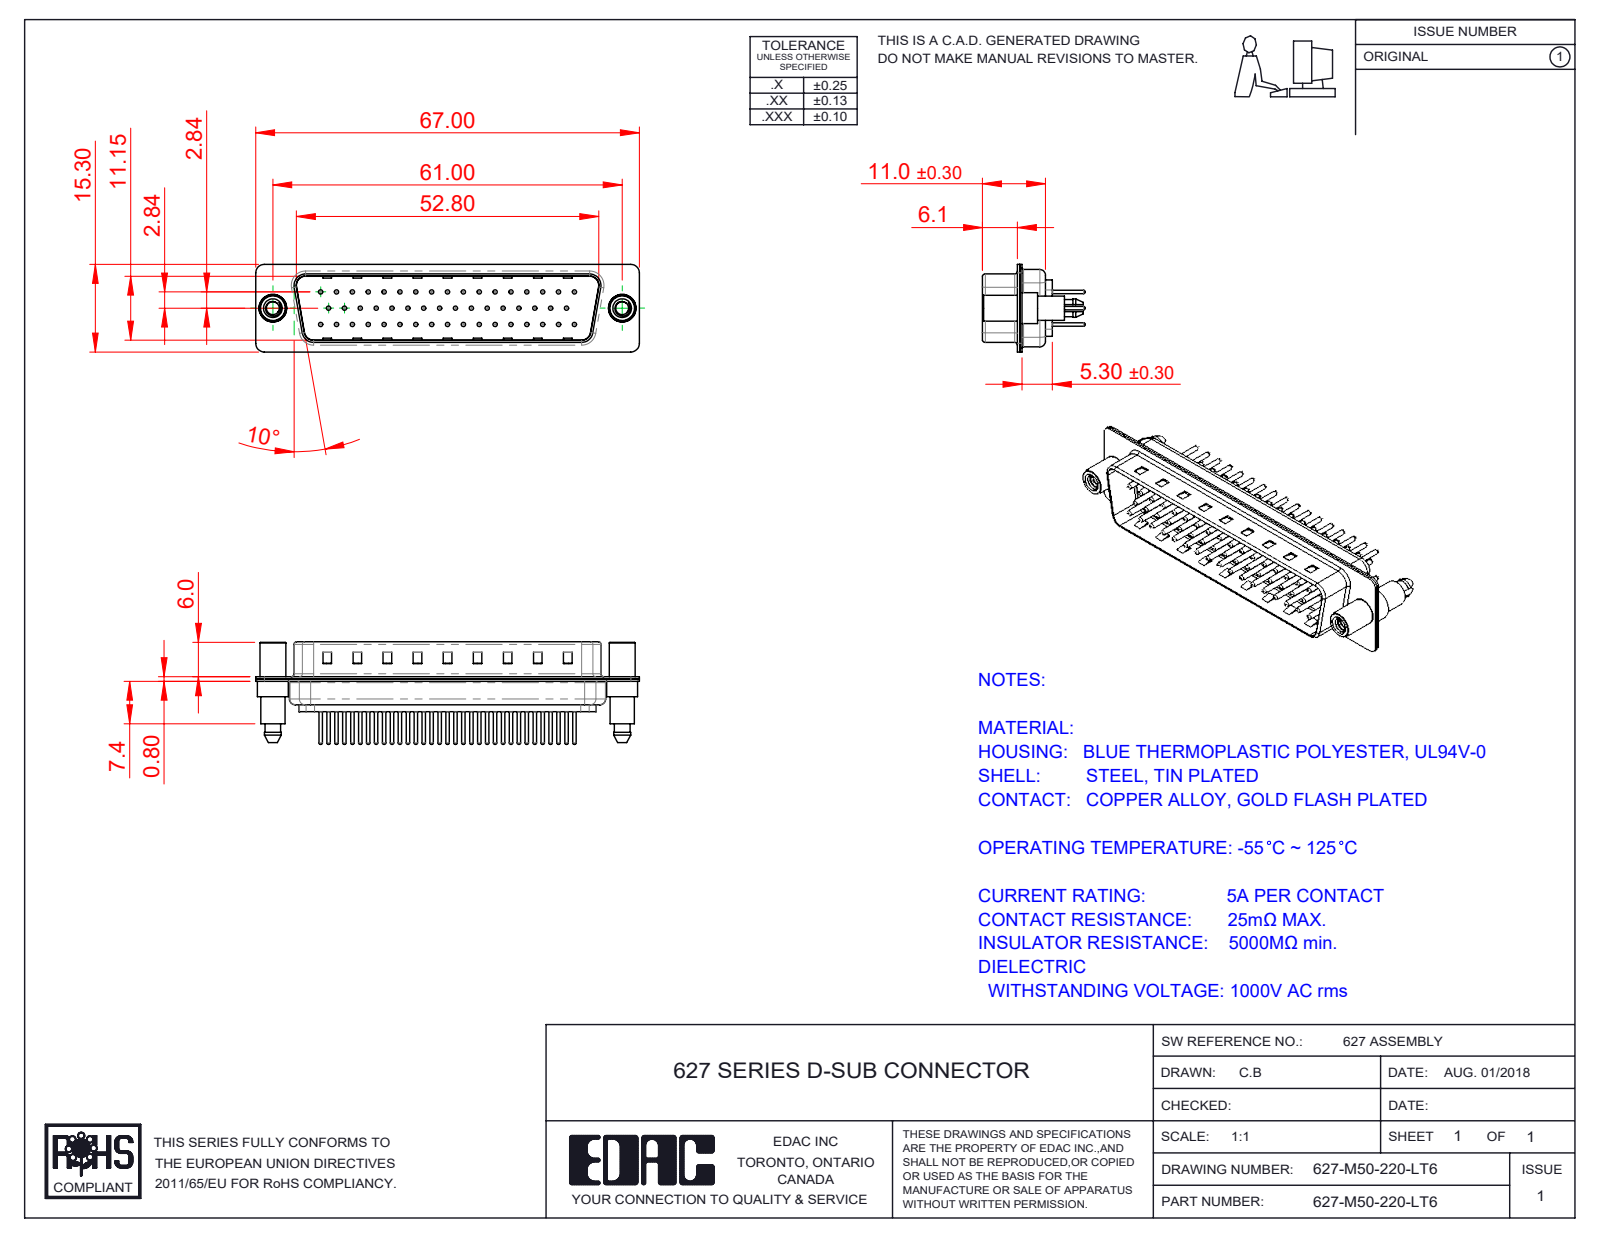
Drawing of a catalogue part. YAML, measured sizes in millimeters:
part_name: "627M Shell Rear_50 Contacts; 627M Contact Row 3_20; 627M Contact Row 1_20; 627M Housing_50 Contacts (+4 more)"
step_written_by: "SolidWorks 2020 (CONFIG_CONTROL_DESIGN)"
units: millimeters
bodies: {solids: 55, faces: 2314, planar: 571, cylindrical: 869, other: 874}
overall_size: [67, 17.9, 15.3]
volume: 4863
surface_area: 11167
round_holes:
  - {diameter: 0.75, count: 50}
  - {diameter: 1.6, count: 50}
  - {diameter: 2, count: 50}
  - {diameter: 2.26, count: 2}
  - {diameter: 4, count: 2}
  - {diameter: 4.8, count: 2}
round_bosses_or_shafts:
  - {diameter: 1.5, count: 50}
  - {diameter: 0.6, count: 50}
  - {diameter: 5.4, count: 2}
  - {diameter: 4.9, count: 2}
  - {diameter: 4.5, count: 2}
  - {diameter: 4.25, count: 2}
partial_cylinders:
  - {radius: 1.5, count: 18}
  - {radius: 2, count: 12}
  - {radius: 1.6, count: 10}
  - {radius: 0.5, count: 8}
  - {radius: 0.25, count: 4}
  - {radius: 0.6, count: 4}
  - {radius: 0.65, count: 4}
  - {radius: 0.9, count: 4}
face_to_face_distances: [0.4, 11.55, 5.7, 6.1, 0.78, 0.77, 12.33, 5.3, 12.32, 13.1]
hole_center_spacings: [3.16, 2.77, 5.54, 8.31, 11.08, 13.85, 16.62, 5.03]
